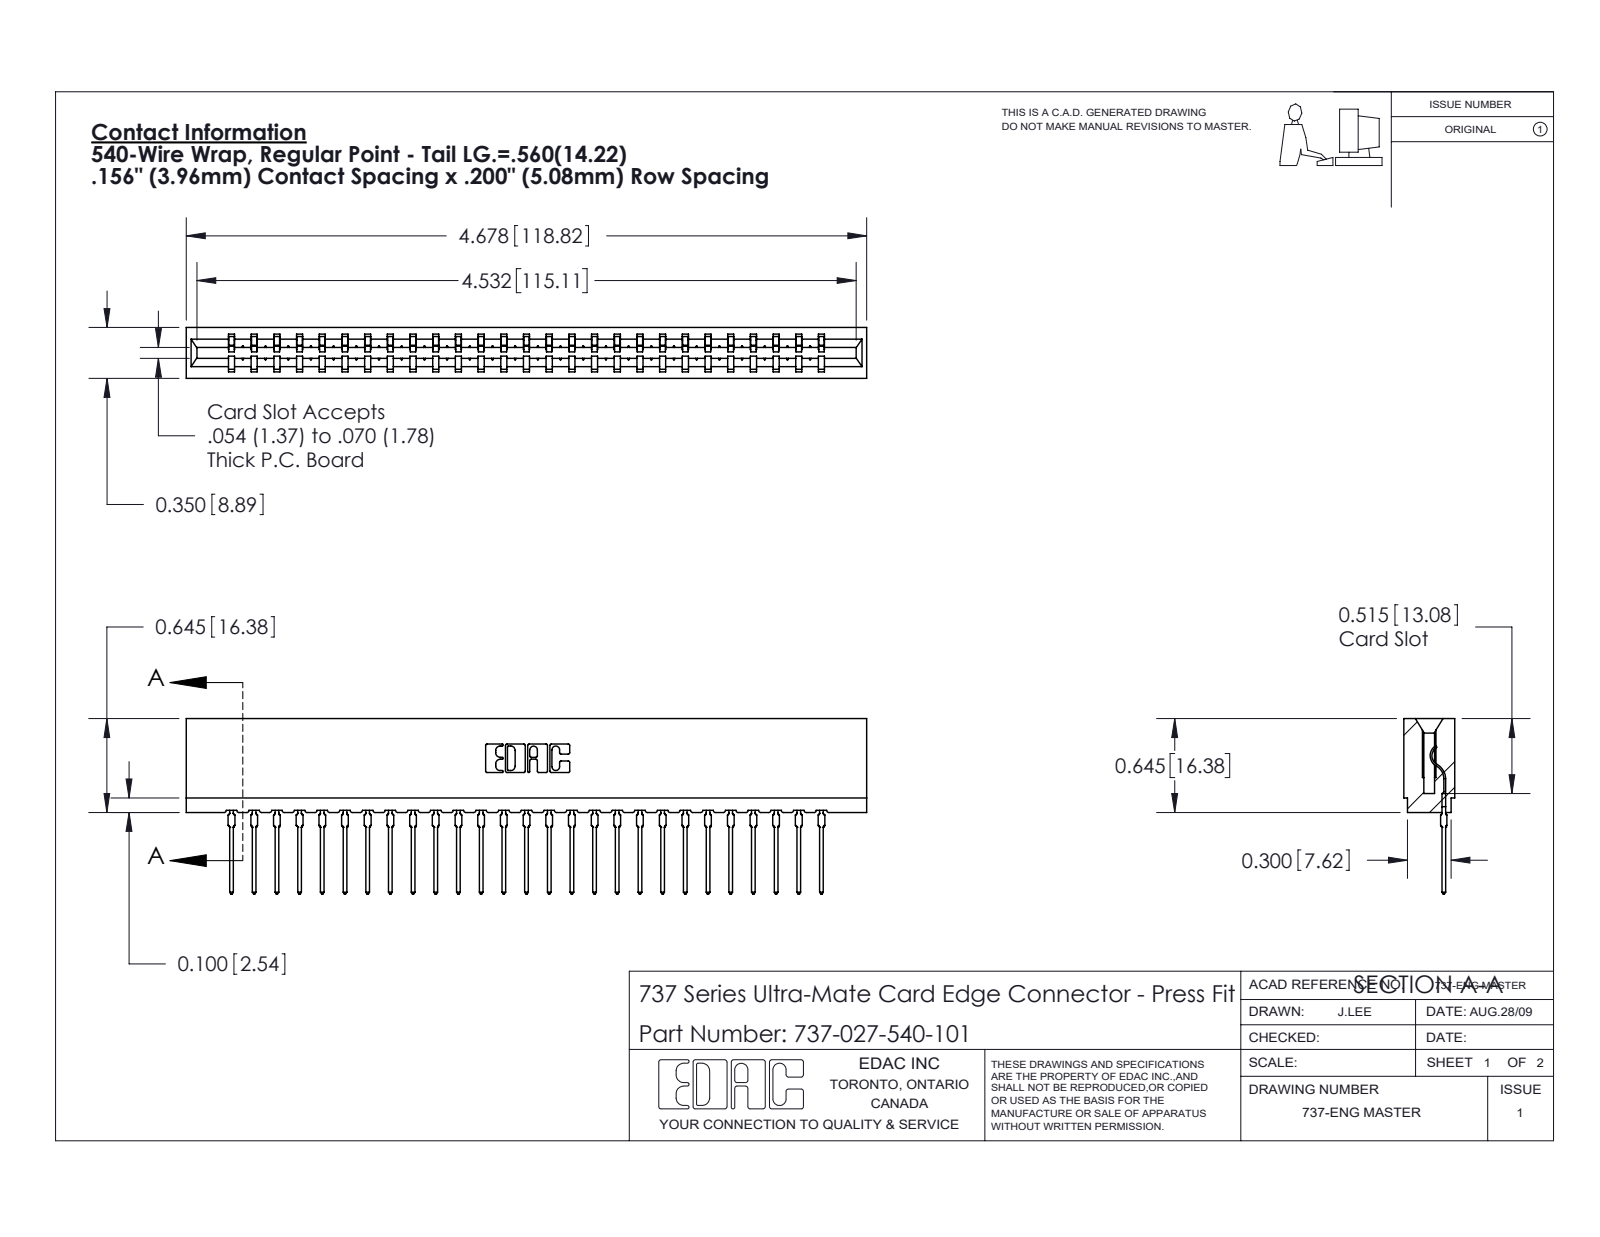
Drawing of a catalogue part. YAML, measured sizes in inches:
part_name: "737 Part_Insulator Option - 01; 737-027-540-101; 745-292-001_540"
step_written_by: "SolidWorks 2020 (CONFIG_CONTROL_DESIGN)"
units: inches
bodies: {solids: 28, faces: 3145, planar: 1890, cylindrical: 553, other: 702}
overall_size: [4.678, 1.206, 0.35]
volume: 0.711
surface_area: 24.34
partial_cylinders:
  - {radius: 0.015, count: 54}
  - {radius: 0.021, count: 54}
  - {radius: 0.01, count: 22}
  - {radius: 0.007, count: 6}
  - {radius: 0.031, count: 6}
  - {radius: 0.005, count: 4}
  - {radius: 0.011, count: 4}
  - {radius: 0.026, count: 3}
face_to_face_distances: [0.138, 0.212, 0.35, 0.624, 0.156, 0.074, 0.78, 0.045, 0.305, 0.093]
